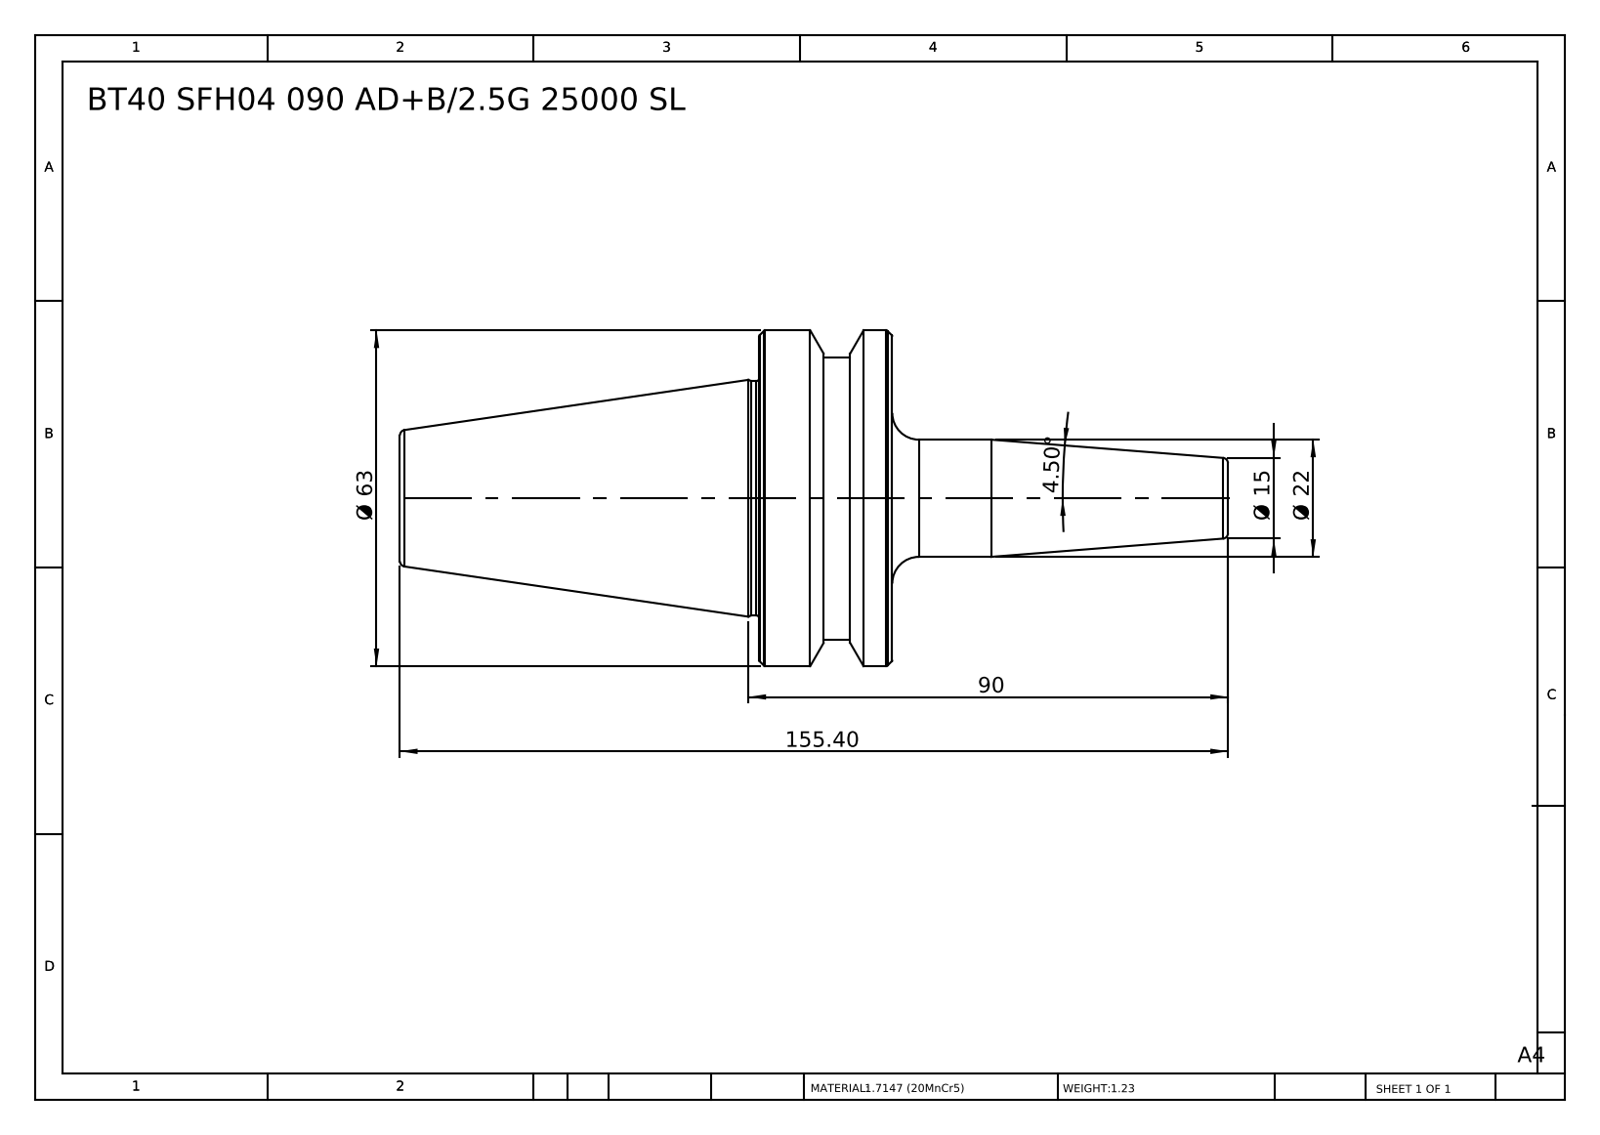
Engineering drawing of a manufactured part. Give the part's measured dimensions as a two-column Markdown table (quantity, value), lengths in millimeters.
| quantity | value |
| --- | --- |
| part name | BT40 SFH04 090 AD+B-2.5G 25000 SL |
| STEP written by | SolidWorks 2014 (CONFIG_CONTROL_DESIGN) |
| units | millimeters |
| bodies | 1 solid, 46 faces (6 planar, 10 cylindrical, 30 other) |
| overall size | 155.4 × 63 × 63 |
| volume | 157 882 mm³ |
| surface area | 21 836 mm² |
| round bosses / shafts (diameter × count) | 63 × 1, 53 × 1, 44 × 1, 22 × 1 |
| main face-to-face distances | 25, 92.4, 67.4, 63, 88, 155.4, 70.9, 7.9, 17.1, 84.5 |
